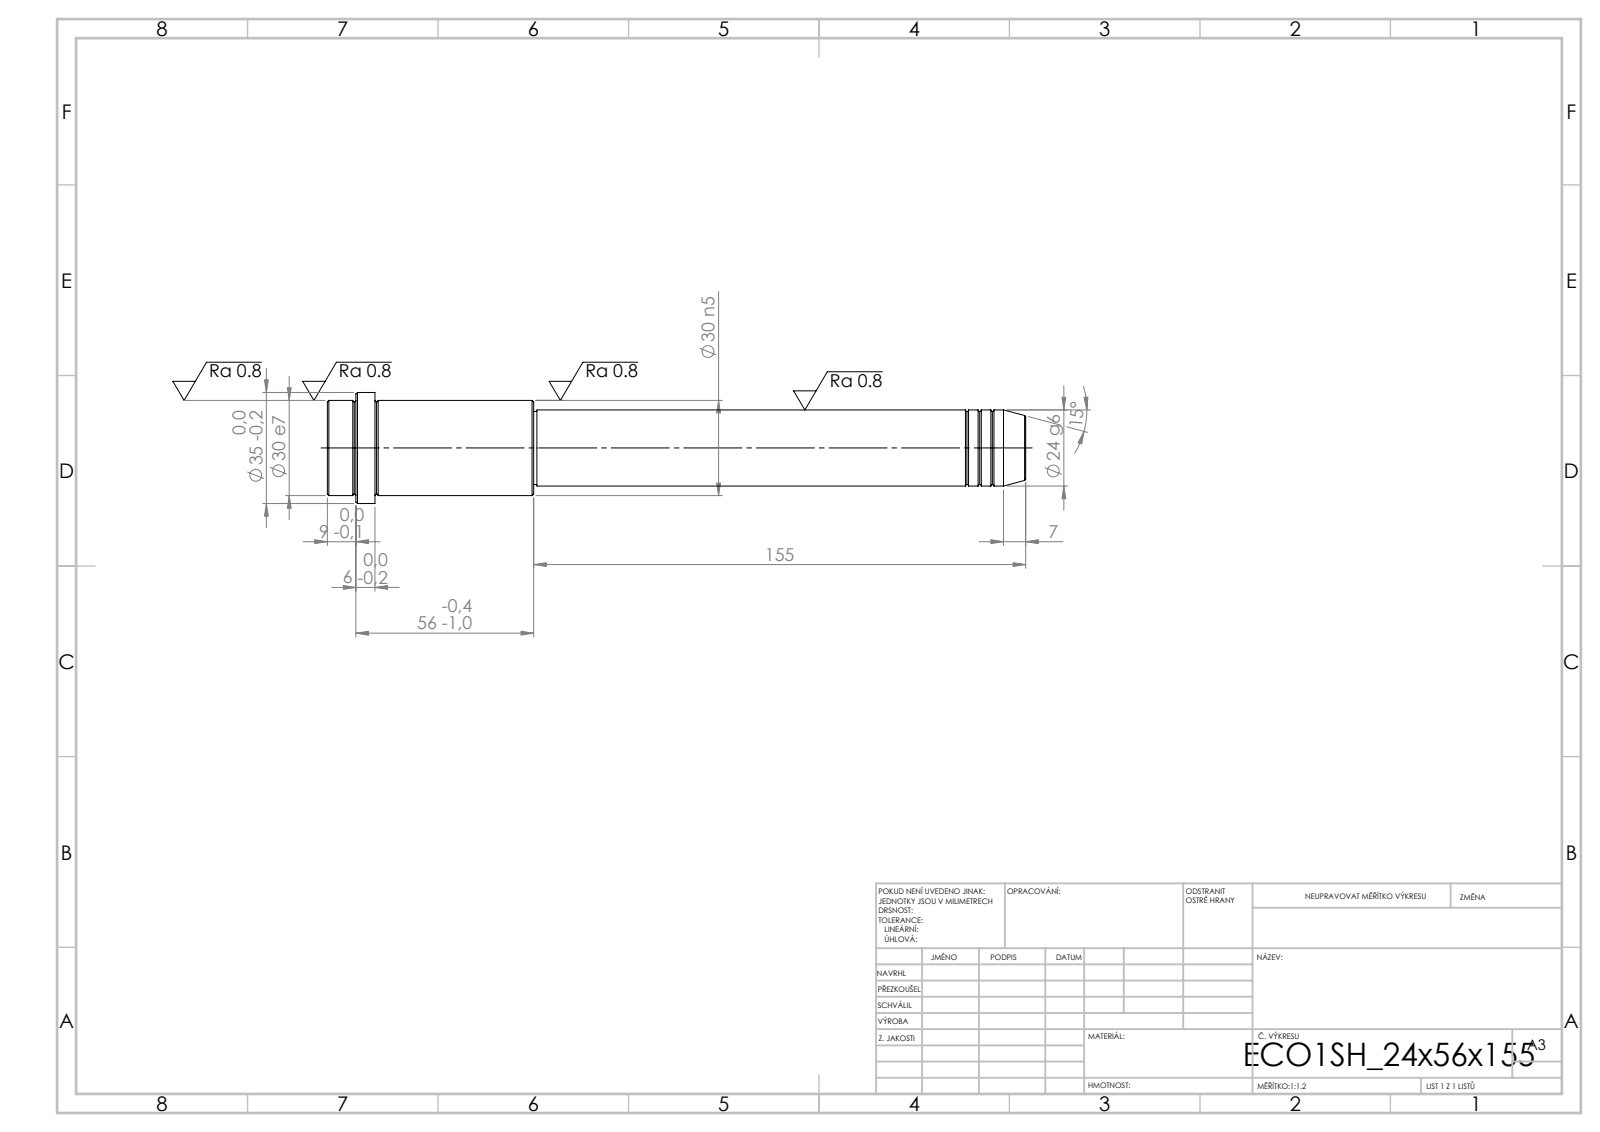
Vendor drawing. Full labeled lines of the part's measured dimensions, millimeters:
STEP written by: SolidWorks 2019 (CONFIG_CONTROL_DESIGN)
Units: millimetres
Bodies: 1 solid, 52 faces (6 planar, 16 cylindrical, 30 other)
Overall size (bounding box): 220 × 35 × 35
Volume: 116 893 mm³ · Surface area: 19 873 mm²
Round bosses / shafts (diameter × count): ⌀35 ×1, ⌀30 ×1, ⌀24 ×1, ⌀23 ×1
Main face-to-face distances: 220, 205, 15, 155, 50, 65, 211, 56, 6, 9
